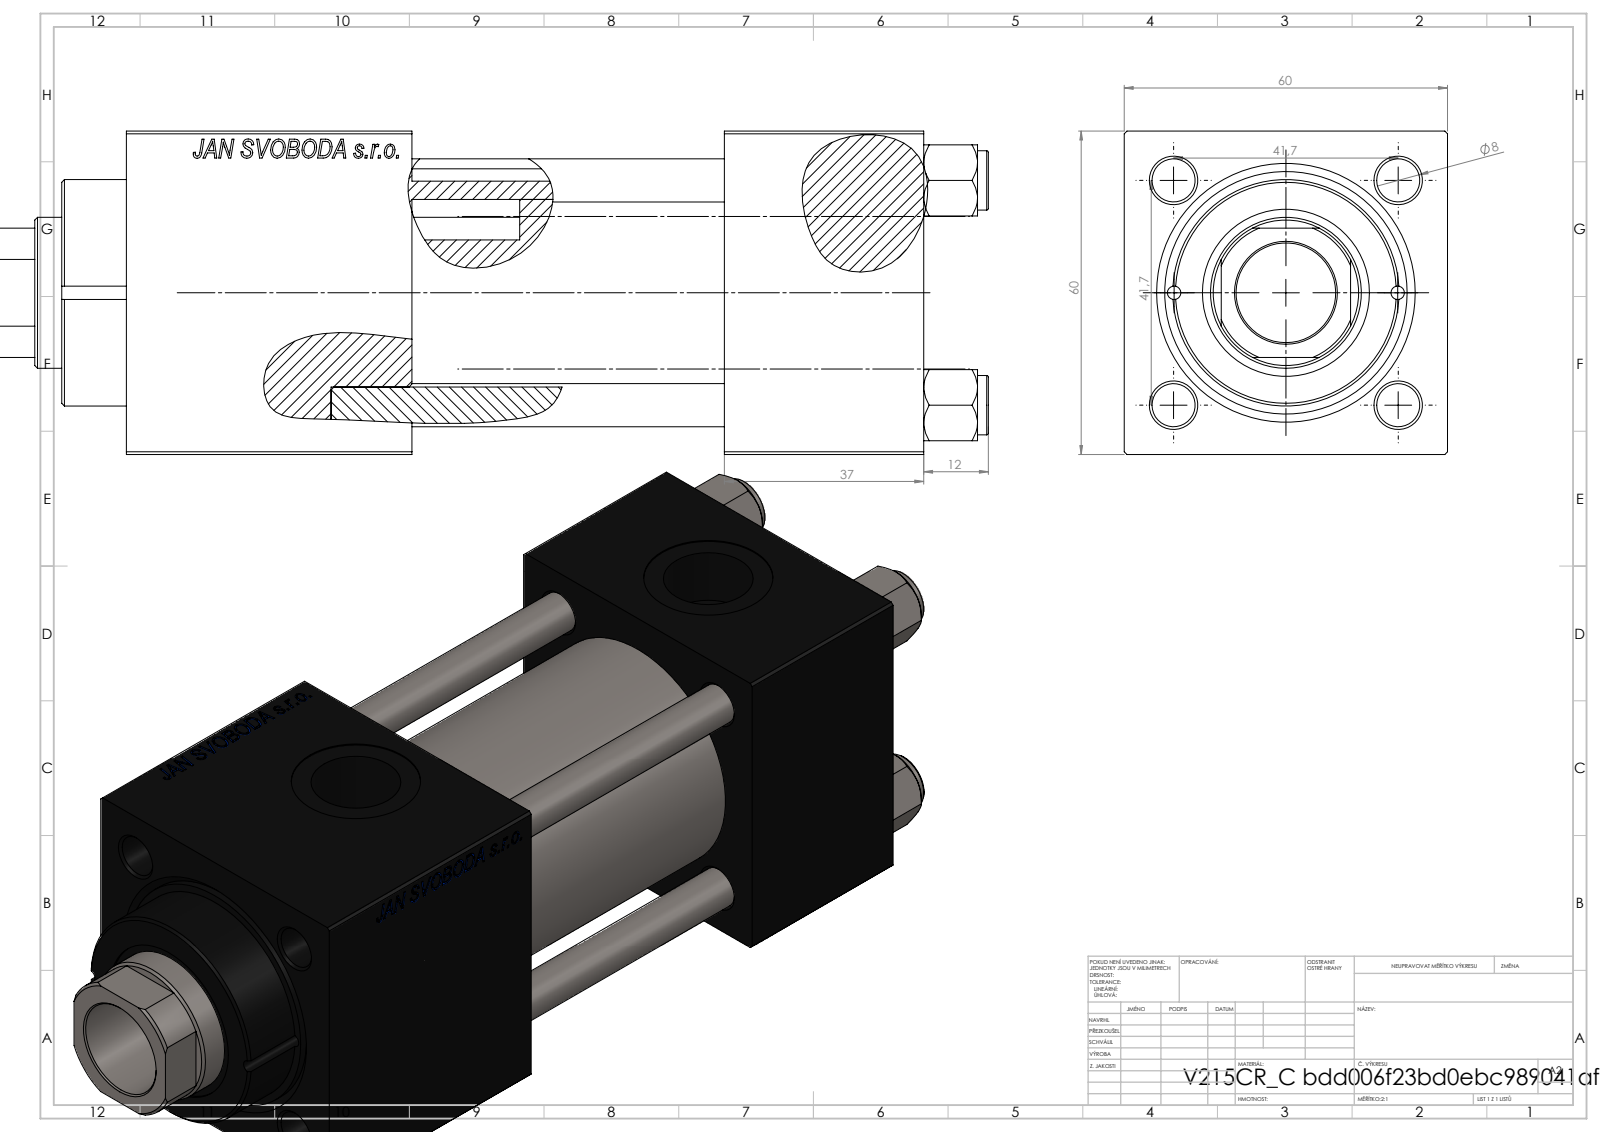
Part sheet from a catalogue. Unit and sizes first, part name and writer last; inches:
Units: inches
Overall size (bounding box): 7.283 × 2.362 × 2.362
Round holes (diameter × count): ⌀0.315 ×4, ⌀0.098 ×2, ⌀0.276 ×2, ⌀0.656 ×2, ⌀0.945 ×2, ⌀0.728 ×1, ⌀1.102 ×1, ⌀1.22 ×1, ⌀1.575 ×1, ⌀1.772 ×1
Round bosses / shafts (diameter × count): ⌀0.433 ×4, ⌀1.811 ×1, ⌀1.654 ×1
Partial cylindrical surfaces — rounded edges, fillets, slot ends (radius × count): R0.531 ×1
Main face-to-face distances: 2.362, 1.457, 2.283, 3.74, 2.087, 4.697, 3.24, 0.957, 5.827, 4.37
Hole centre spacings: 0.821, 1.161, 1.642, 1.832, 0.817, 2.322, 1.634, 3.642
Volume: 25.87 in³ · Surface area: 172.9 in²
Bodies: 11 solids, 1155 faces (528 planar, 91 cylindrical, 536 other)
Part name (STEP PRODUCT): V215CR_C_TYCINKA; V215CR_C_Body; NUT_M5_C; V215CR_VCP_C (+1 more)
STEP written by: SolidWorks 2019 (CONFIG_CONTROL_DESIGN)
